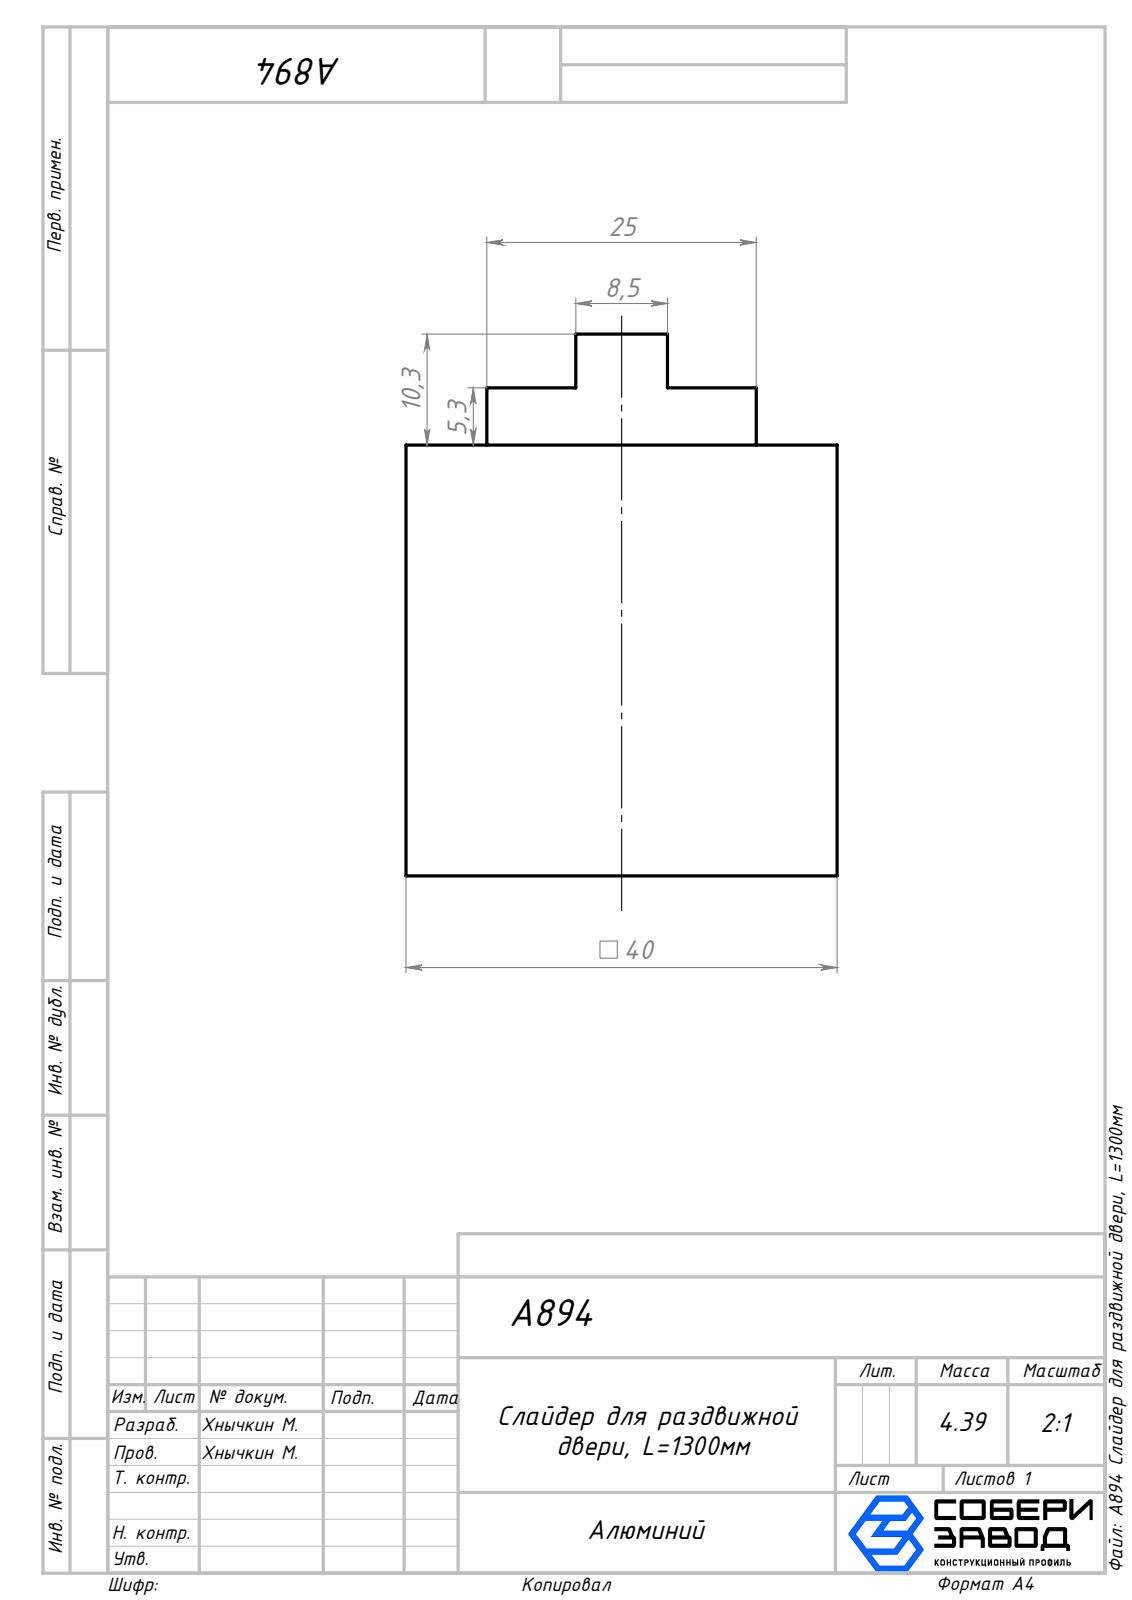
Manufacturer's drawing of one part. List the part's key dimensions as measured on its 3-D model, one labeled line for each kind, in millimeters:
Part name (STEP PRODUCT): A894 Слайдер для раздвижной двери, L=1300мм
STEP written by: SolidWorks 2026 (AUTOMOTIVE_DESIGN)
Units: millimetres
Bodies: 1 solid, 90 faces (72 planar, 18 cylindrical, 0 other)
Overall size (bounding box): 1310 × 50.3 × 40
Volume: 1 626 000 mm³ · Surface area: 403 348 mm²
Partial cylindrical surfaces — rounded edges, fillets, slot ends (radius × count): R0.25 ×12, R0.5 ×6
Main face-to-face distances: 11, 29, 10, 40, 1, 15, 25, 3, 30, 26
